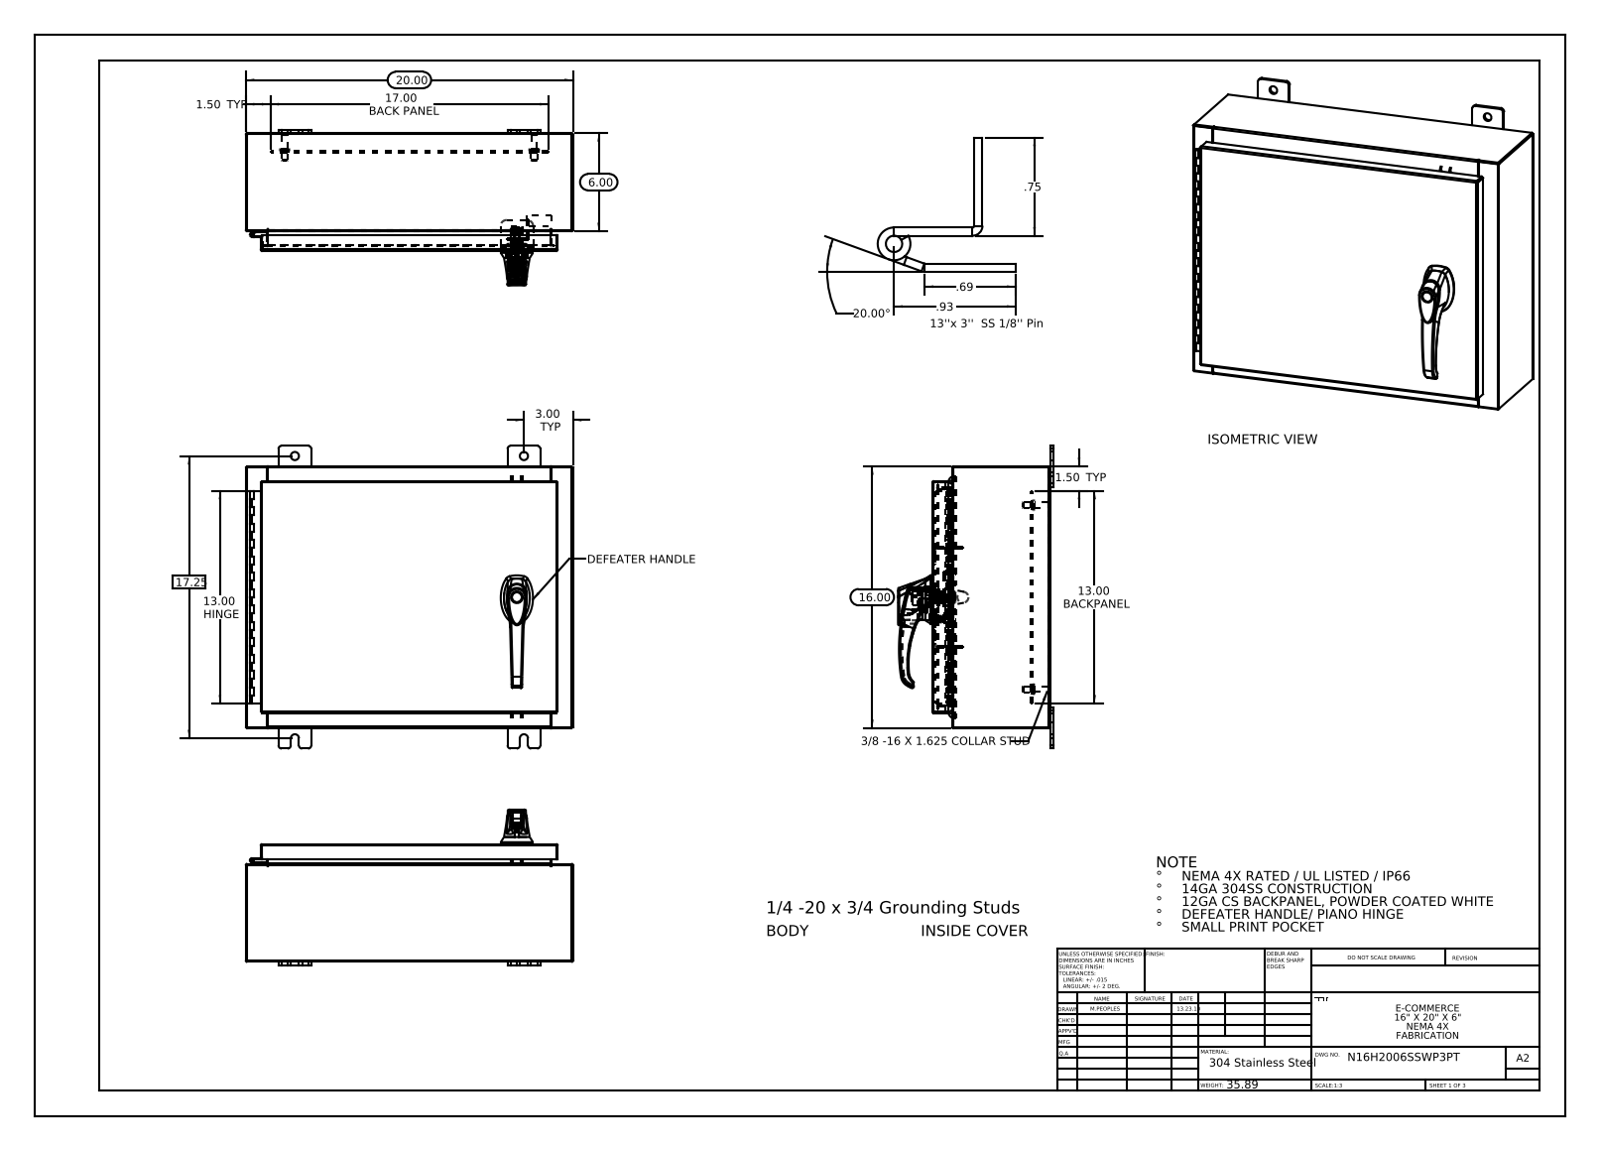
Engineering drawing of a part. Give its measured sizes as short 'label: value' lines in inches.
name: N16H2006SSWP3PT Hinge Enclosure Side2; Quarter-20 CD Stud; N16H2006SSWP3PT Defeater Handle - 3 - 2500-51 ZN; N16H2006SSWP3PT Hinge Cover Side (+8 more)
written by: SolidWorks 2013 (CONFIG_CONTROL_DESIGN)
unit: in
bodies: 37 solids, 2290 faces (775 planar, 817 cylindrical, 698 other)
size: 20 × 18.5 × 9.495
volume: 128.6 in³; area: 3 157 in²
holes: 8× ⌀0.5, 4× ⌀0.25, 3× ⌀0.138, 3× ⌀0.161, 2× ⌀0.079, 2× ⌀0.203, 2× ⌀0.313, 2× ⌀0.437, 1× ⌀0.125, 1× ⌀0.125, 1× ⌀0.197, 1× ⌀0.276
bosses: 4× ⌀0.625, 4× ⌀0.375, 4× ⌀0.33, 4× ⌀0.157, 4× ⌀0.14, 3× ⌀0.315, 3× ⌀0.236, 1× ⌀1.181
rounds: 37× R0.118, 33× R0.006, 24× R0.19, 20× R0.013, 18× R0.088, 15× R0.039, 12× R0.028, 6× R0.008
face distances: 0.075, 7.126, 7.051, 7.201, 15.925, 1, 0.104, 1.075, 6.051, 6.126
hole spacings: 3.708, 0.295, 0.625, 0.841, 1.25, 1.313, 1.32, 1.484
